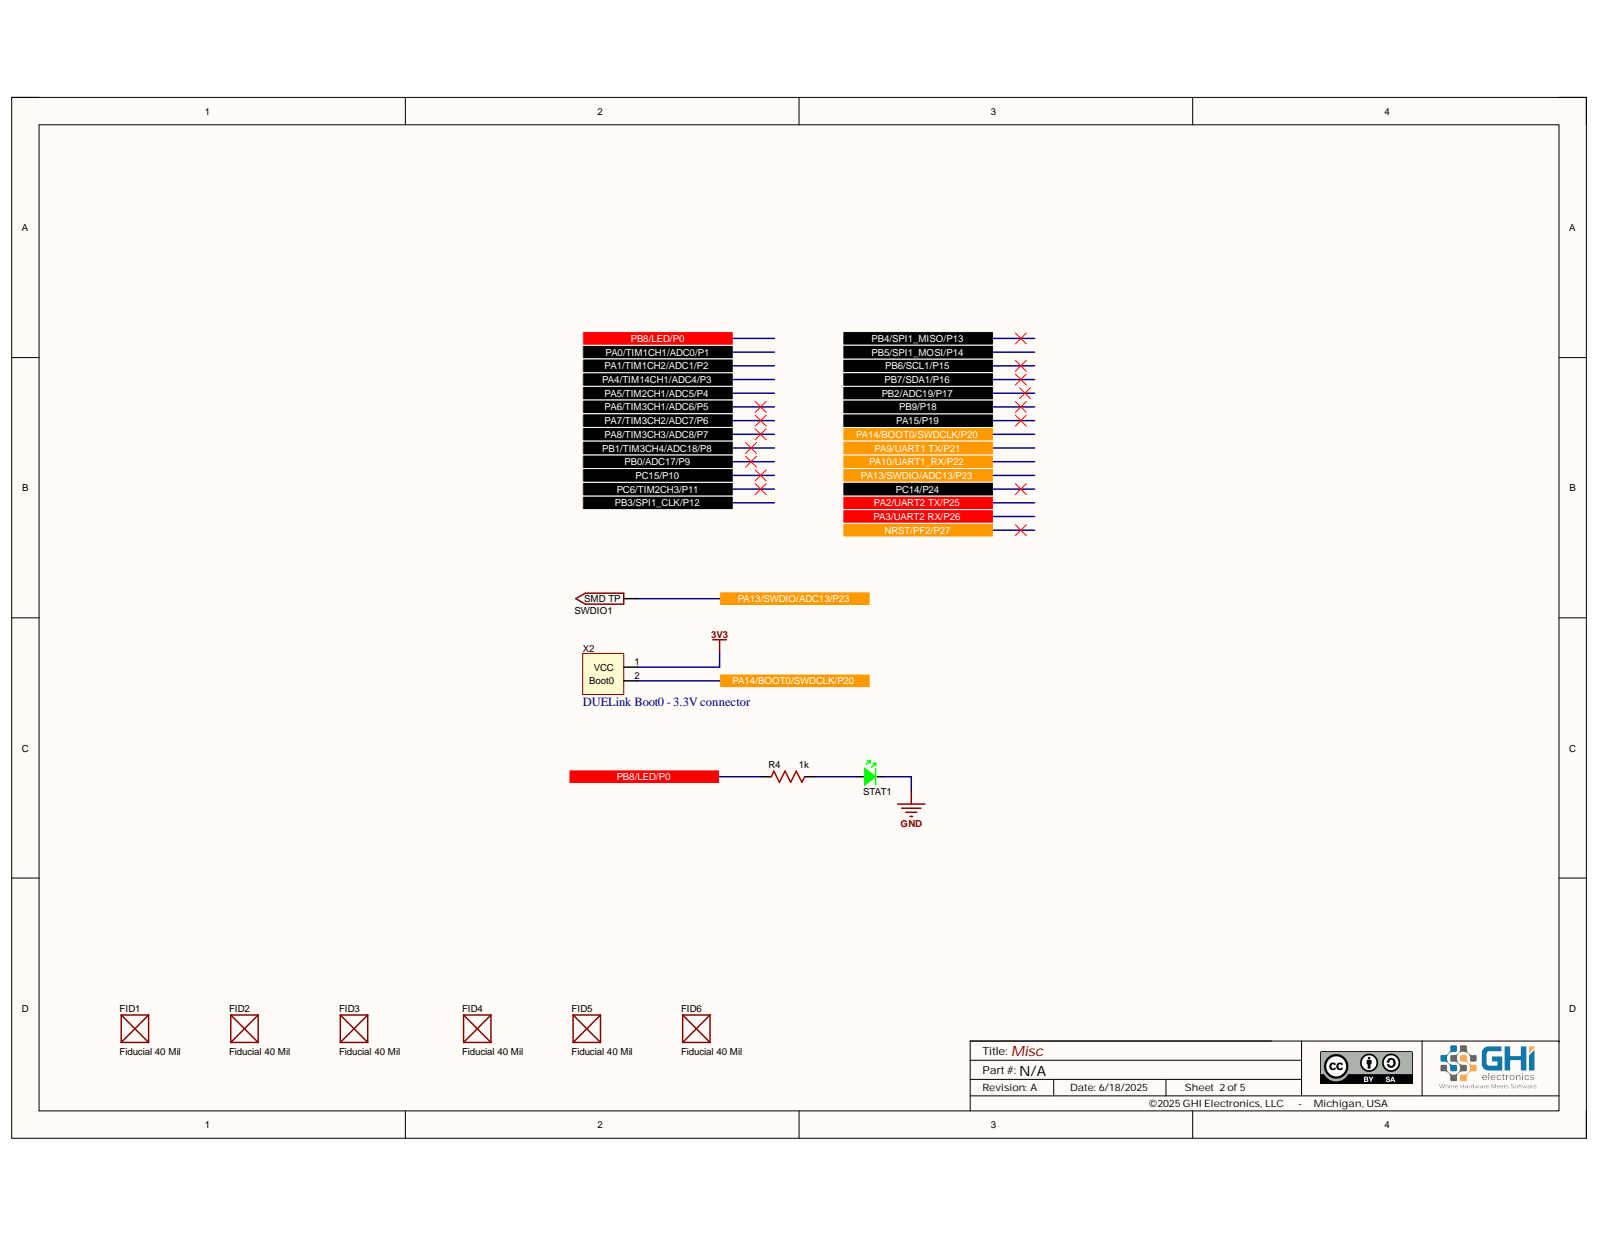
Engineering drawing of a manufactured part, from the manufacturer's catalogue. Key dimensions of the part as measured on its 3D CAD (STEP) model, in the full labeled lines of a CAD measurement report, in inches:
Part name (STEP PRODUCT): PCB; Board; C3; 0805 SMD Capacitor (+6 more)
STEP written by: Open CASCADE 7.5 (AUTOMOTIVE_DESIGN)
Units: inches
Bodies: 83 solids, 1721 faces (1346 planar, 232 cylindrical, 143 other)
Overall size (bounding box): 4.213 × 3.445 × 0.72
Volume: 3.847 in³ · Surface area: 59.64 in²
Round holes (diameter × count): ⌀0.04 ×8, ⌀0.118 ×4, ⌀0.04 ×2
Partial cylindrical surfaces — rounded edges, fillets, slot ends (radius × count): R0.005 ×35, R0.006 ×26, R0.138 ×4, R0.007 ×2, R0.007 ×2, R0.007 ×2
Main face-to-face distances: 0.063, 0.236, 0.079, 0.142, 0.378, 0.315, 3.445, 3.602, 0.305, 3.907
Hole centre spacings: 0.1, 0.141, 0.2, 0.224, 0.3, 0.316, 1.819, 1.82
